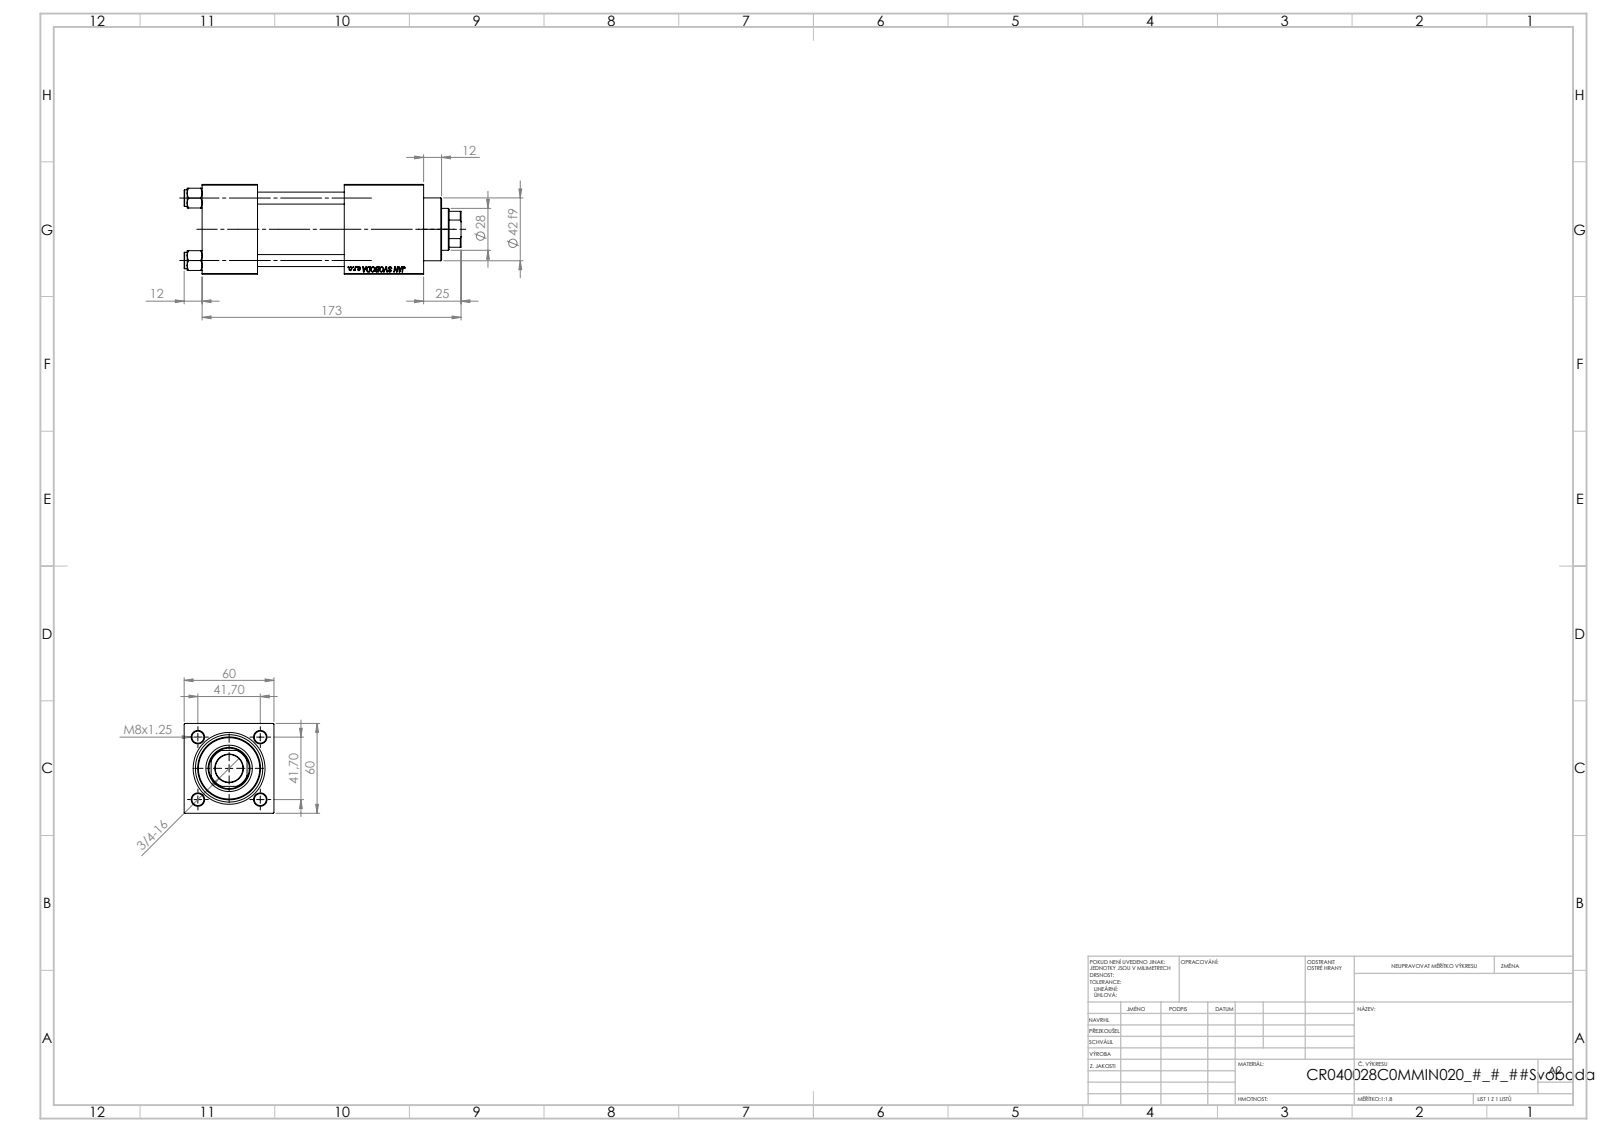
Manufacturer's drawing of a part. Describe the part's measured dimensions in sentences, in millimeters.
The part is named "V215CR_VCP_C; NUT_M5_C; V215_VC_A; V215CR_C_TYCINKA (+1 more)". Its 3-D file was written by "SolidWorks 2019 (CONFIG_CONTROL_DESIGN)". It is 11 solids with 1148 faces: 526 planar, 86 cylindrical and 536 other. Overall it measures 185 by 60 by 60 millimeters. Its volume is 424 489 cubic millimeters and its surface area 111 347 square millimeters. Round holes: 4 of diameter 8, 2 of diameter 7, 2 of diameter 16.66, 2 of diameter 24, 1 of diameter 18.5, 1 of diameter 28, 1 of diameter 31, 1 of diameter 40, 1 of diameter 45. Round bosses or shafts: 4 of diameter 11, 1 of diameter 46, 1 of diameter 42. Partial cylindrical surfaces (rounded edges, fillets, slot ends): 1 of radius 13.5. The main face-to-face distances are 60, 37, 58, 95, 53, 119.3, 82.3, 24.3, 148, 111. The hole center spacings are 29.49, 41.7, 58.97, 92.5.
